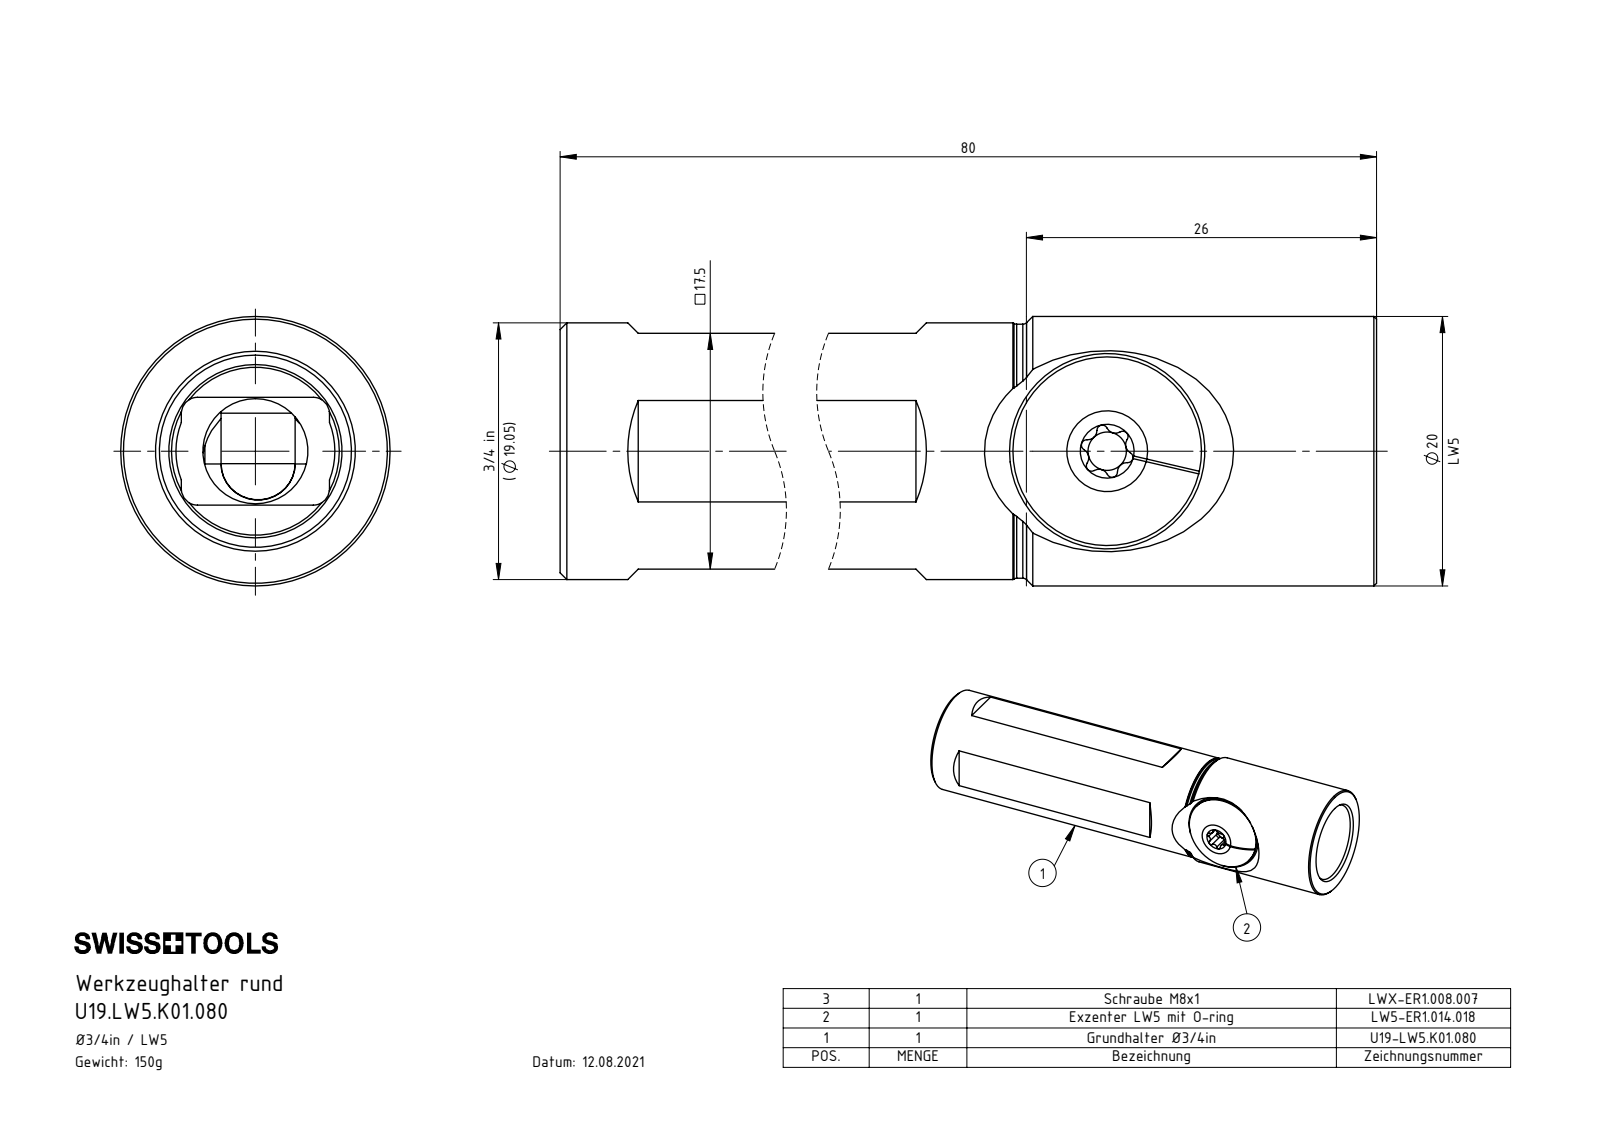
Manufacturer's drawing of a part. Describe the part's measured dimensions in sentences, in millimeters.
The part is named "LW5-ER1.014.018; U19-LW5.K01.080_A; DIN 3771 - 10x1; U19.LW5.K01.080 (+1 more)". Its 3-D file was written by "SolidWorks 2017 (AUTOMOTIVE_DESIGN)". It is 4 solids with 141 faces: 53 planar, 45 cylindrical and 43 other. Overall it measures 80 by 20 by 20 millimeters. Its volume is 17 988 cubic millimeters and its surface area 8 741 square millimeters. Round holes: 1 of diameter 1, 1 of diameter 2.85, 1 of diameter 7, 1 of diameter 7.8, 1 of diameter 12.86. Round bosses or shafts: 1 of diameter 20, 1 of diameter 19.05, 1 of diameter 14, 1 of diameter 12, 1 of diameter 10.2. Partial cylindrical surfaces (rounded edges, fillets, slot ends): 6 of radius 0.4, 6 of radius 0.69, 4 of radius 1.2, 2 of radius 2.75, 2 of radius 4.15, 1 of radius 4.1, 1 of radius 4.7, 1 of radius 5.9. The main face-to-face distances are 17.5, 80, 0.55, 16.95, 12.1, 2.35, 13.2, 15.15, 14.6, 1.4.
